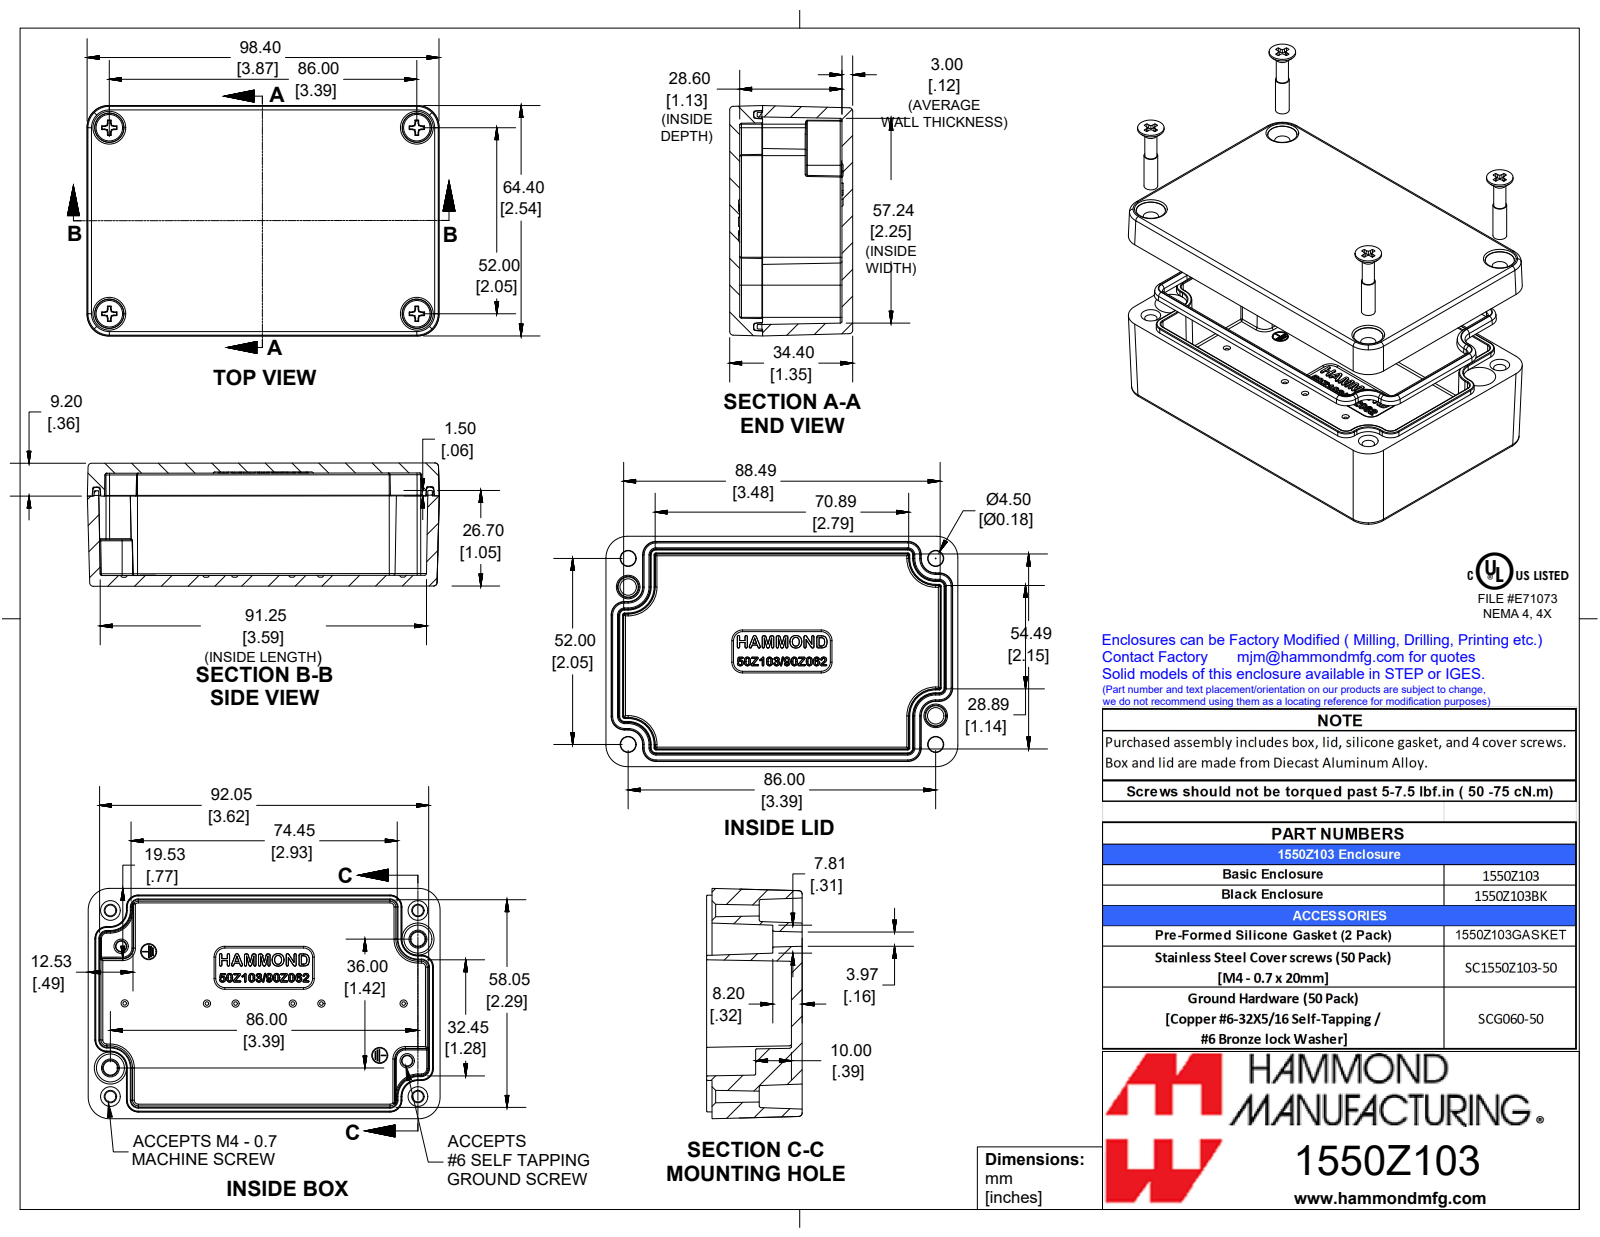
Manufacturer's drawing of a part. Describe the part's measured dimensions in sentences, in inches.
The part is named "1550Z103-1590Z062". Its 3-D file was written by "SolidWorks 2019 (AUTOMOTIVE_DESIGN)". It is 7 solids with 1535 faces: 401 planar, 224 cylindrical and 910 other. Overall it measures 3.874 by 2.535 by 1.354 inches. Its volume is 4.573 cubic inches and its surface area 81.46 square inches. Round bosses or shafts: 4 of diameter 0.299, 4 of diameter 0.154, 4 of diameter 0.13. Partial cylindrical surfaces (rounded edges, fillets, slot ends): 40 of radius 0.008, 32 of radius 0.012, 30 of radius 0.02, 28 of radius 0.039, 8 of radius 0.236. The main face-to-face distances are 1.354, 1.236, 0.118, 1.244, 1.126, 0.11, 0.992, 0.874, 0.252, 0.362.
